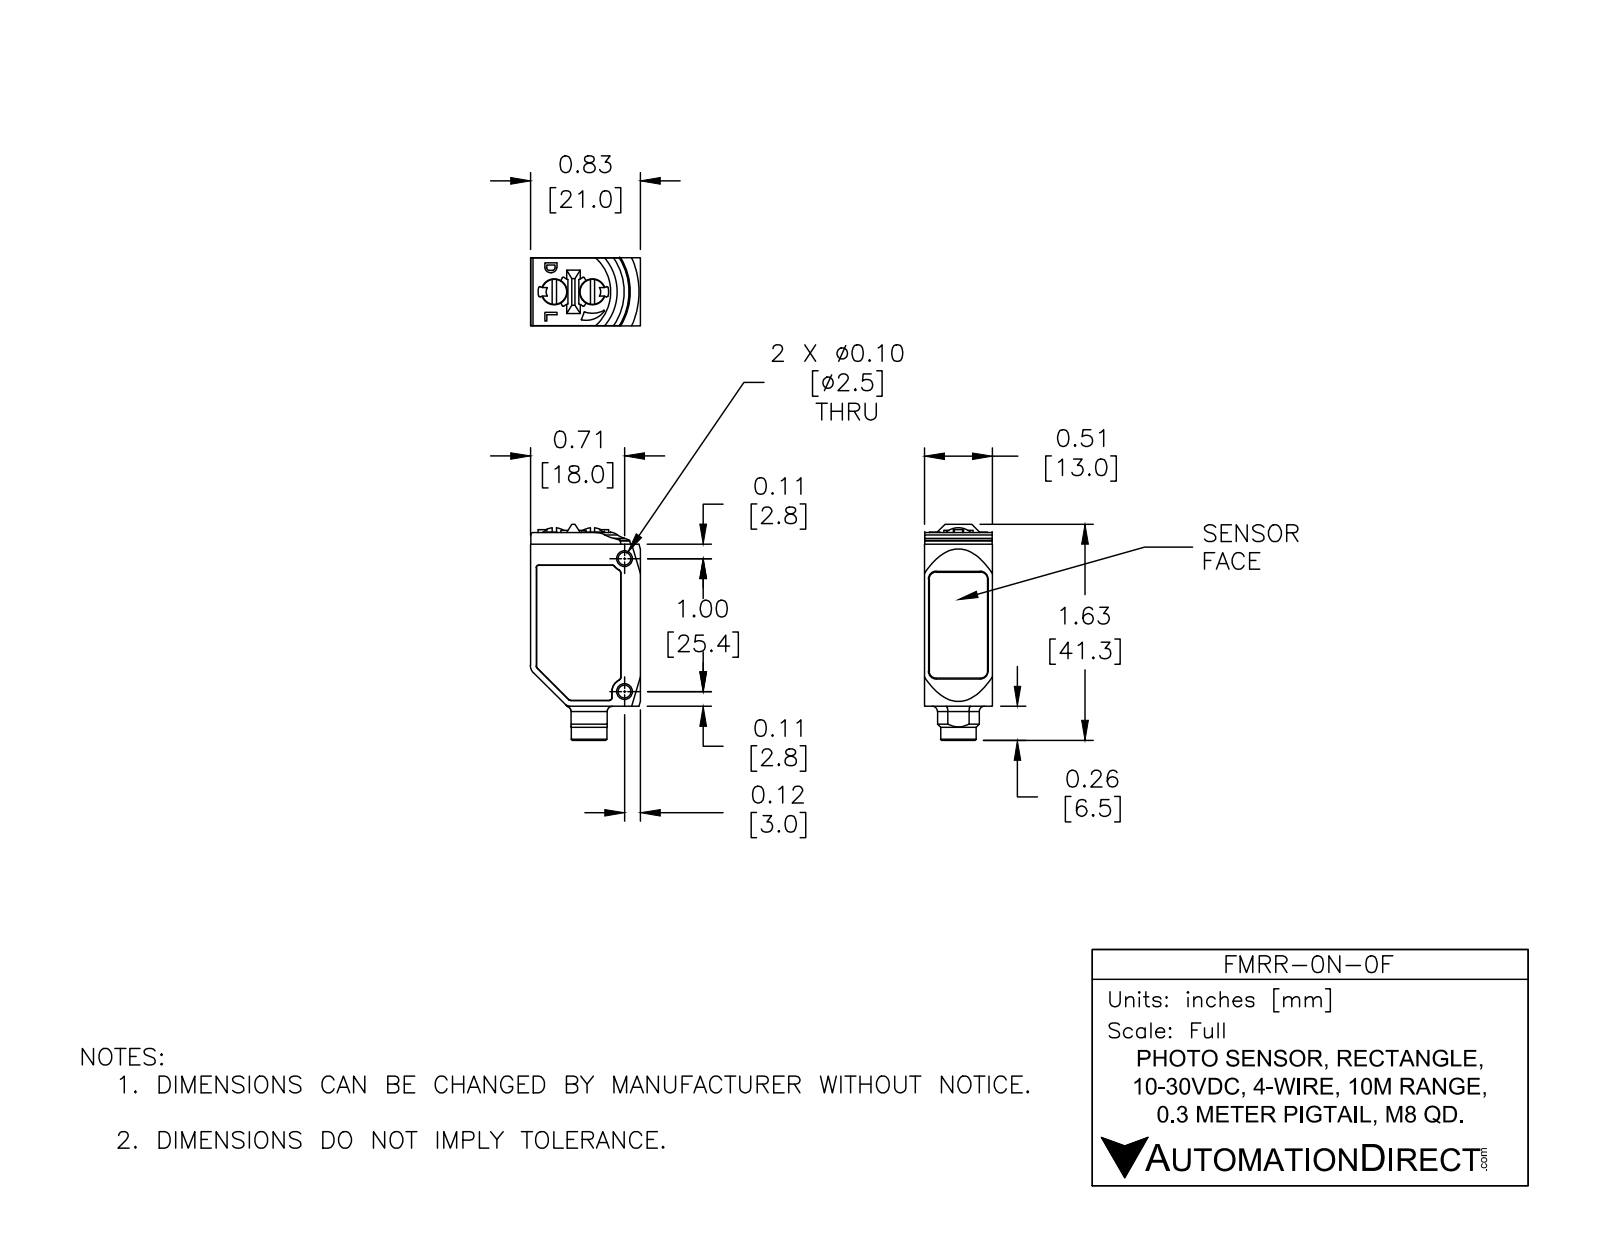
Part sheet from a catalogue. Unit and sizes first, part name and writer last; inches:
Units: inches
Overall size (bounding box): 1.626 × 0.827 × 0.512
Round holes (diameter × count): ⌀0.097 ×2, ⌀0.197 ×2, ⌀0.228 ×1
Round bosses / shafts (diameter × count): ⌀0.189 ×2, ⌀0.267 ×1
Partial cylindrical surfaces — rounded edges, fillets, slot ends (radius × count): R0.018 ×7, R0.02 ×7, R0.039 ×5, R0.008 ×4, R0.01 ×4, R0.051 ×4, R0.059 ×4, R0.004 ×3
Main face-to-face distances: 0.512, 0.827, 1.307, 0.51, 0.031, 0.48, 0.037, 0.035, 0.474, 0.03
Hole centre spacings: 0.026, 0.262, 0.287, 1
Volume: 0.527 in³ · Surface area: 5.26 in²
Bodies: 1 solid, 197 faces (89 planar, 79 cylindrical, 29 other)
Part name (STEP PRODUCT): FMRR-0N-0F
STEP written by: SolidWorks 2017 (AUTOMOTIVE_DESIGN)
